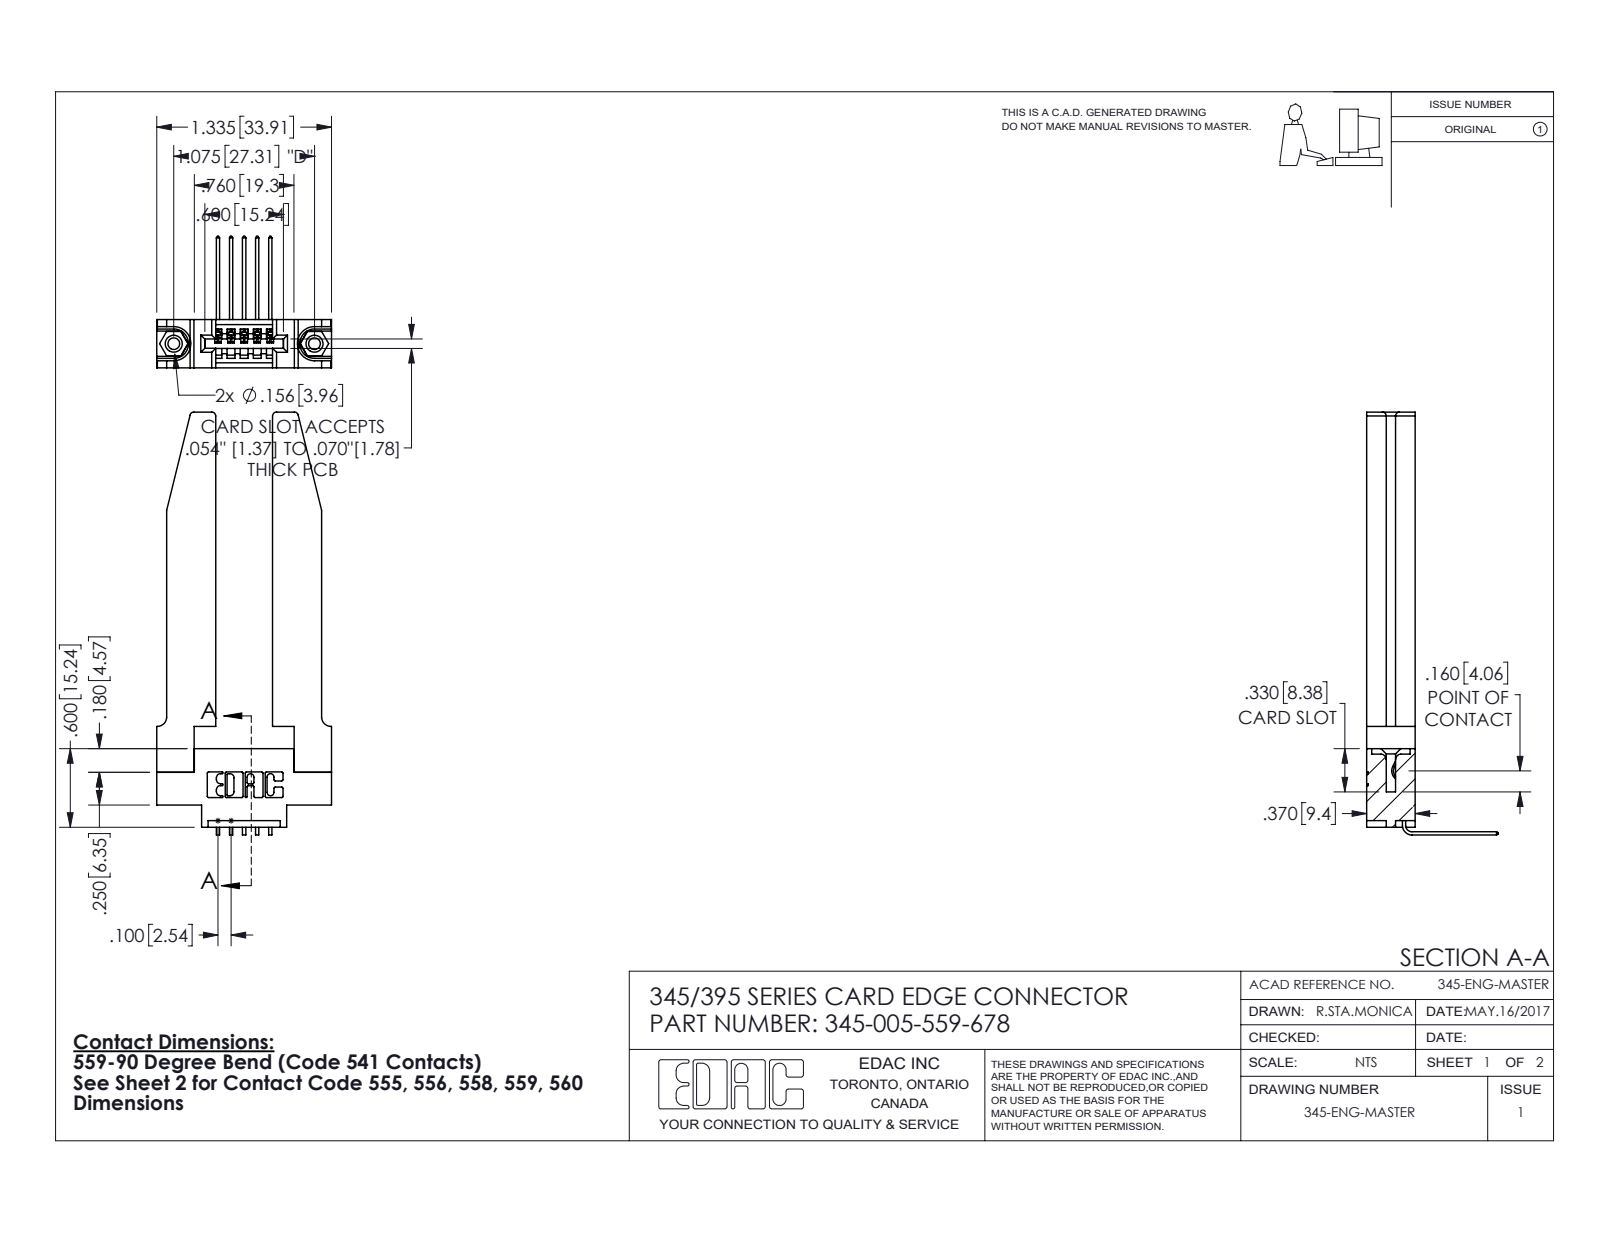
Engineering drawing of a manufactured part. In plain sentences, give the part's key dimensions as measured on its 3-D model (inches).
The part is named "345 Part_0.170 Offset - 0.156 Dia-TH; 345-250-001_345-250-001-102; 345-292-001_558 559 Tail - 1; 345-005-559-678 (+1 more)". Its 3-D file was written by "SolidWorks 2016 (CONFIG_CONTROL_DESIGN)". It is 10 solids with 664 faces: 436 planar, 176 cylindrical and 52 other. Overall it measures 3.229 by 1.336 by 1.005 inches. Its volume is 0.646 cubic inches and its surface area 15.99 square inches. Round holes: 2 of diameter 0.089, 2 of diameter 0.125, 2 of diameter 0.156, 1 of diameter 0.064. Round bosses or shafts: 2 of diameter 0.155. Partial cylindrical surfaces (rounded edges, fillets, slot ends): 22 of radius 0.01, 10 of radius 0.006, 8 of radius 0.03, 6 of radius 0.007, 6 of radius 0.031, 3 of radius 0.026, 2 of radius 0.031, 2 of radius 0.04. The main face-to-face distances are 0.37, 0.15, 0.22, 0.435, 0.072, 0.148, 0.095, 0.298, 0.077, 0.071. The hole center spacings are 0.27, 0.847, 1.075.
